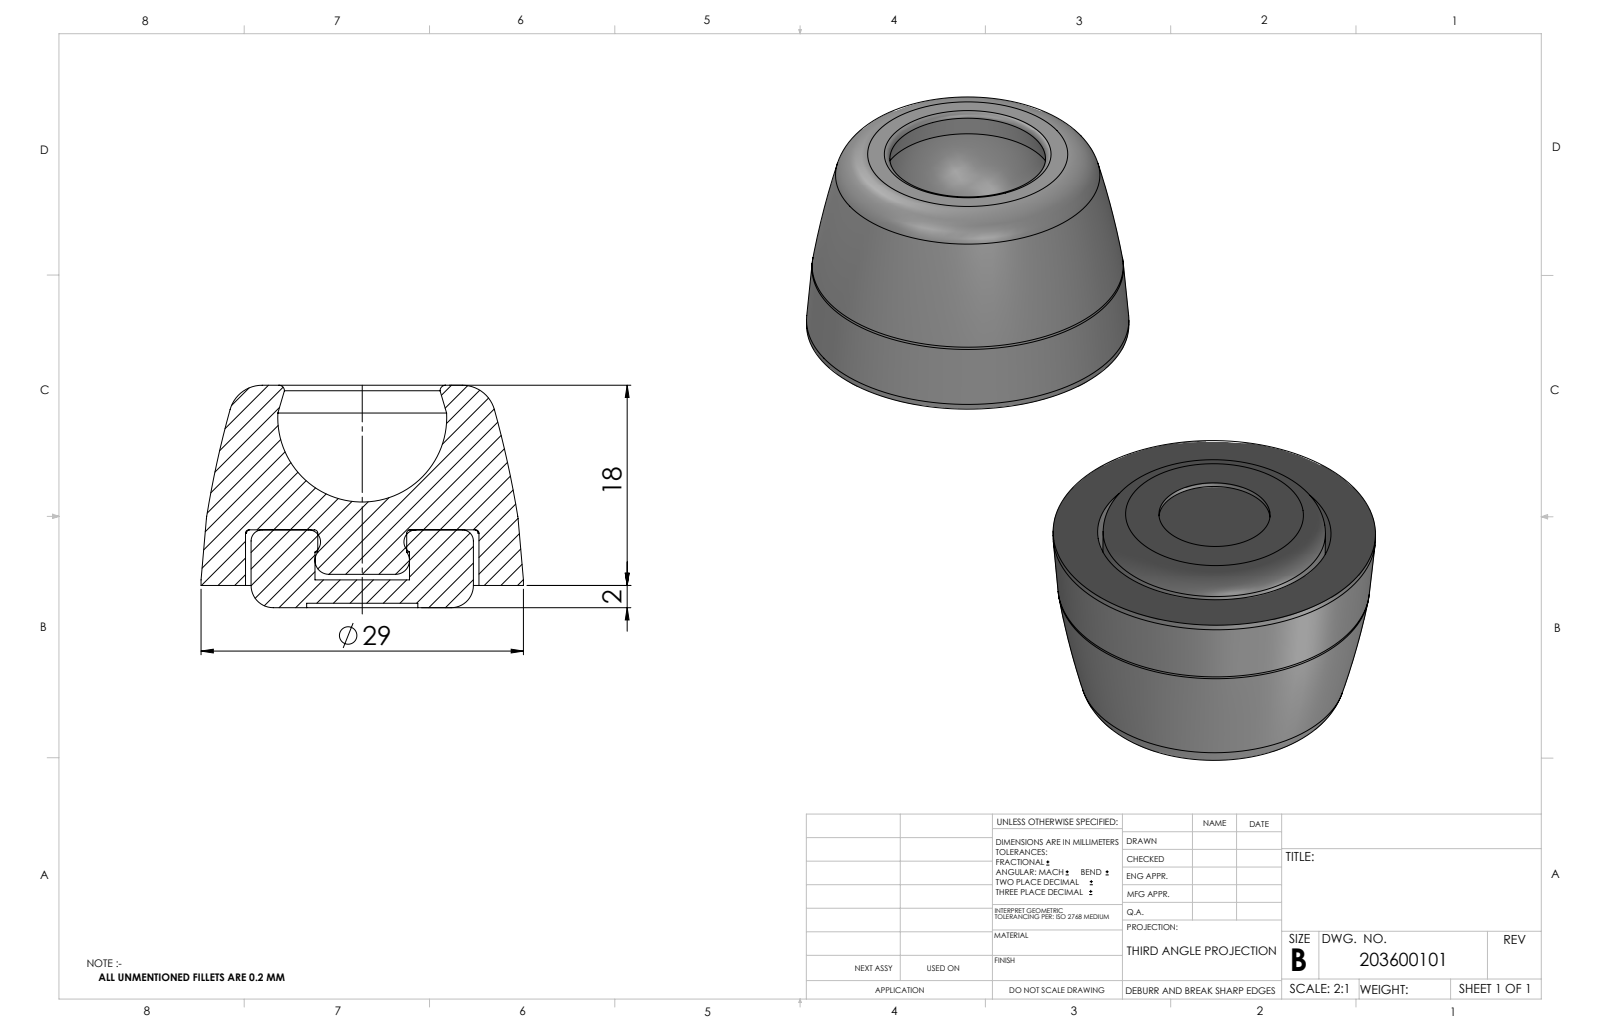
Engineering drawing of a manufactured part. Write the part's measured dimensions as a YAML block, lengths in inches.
part_name: "203600101_c_1"
step_written_by: "SolidWorks 2014 (CONFIG_CONTROL_DESIGN)"
units: inches
bodies: {solids: 2, faces: 158, planar: 31, cylindrical: 12, other: 115}
overall_size: [1.142, 1.142, 0.787]
volume: 0.514
surface_area: 7.457
round_holes:
  - {diameter: 0.335, count: 1}
  - {diameter: 0.394, count: 1}
  - {diameter: 0.827, count: 1}
round_bosses_or_shafts:
  - {diameter: 1.142, count: 1}
  - {diameter: 0.787, count: 1}
  - {diameter: 0.315, count: 1}
face_to_face_distances: [0.197, 0.098, 0.079, 0.276, 0.02, 0.016, 0.063, 0.26, 0.787, 0.772]
